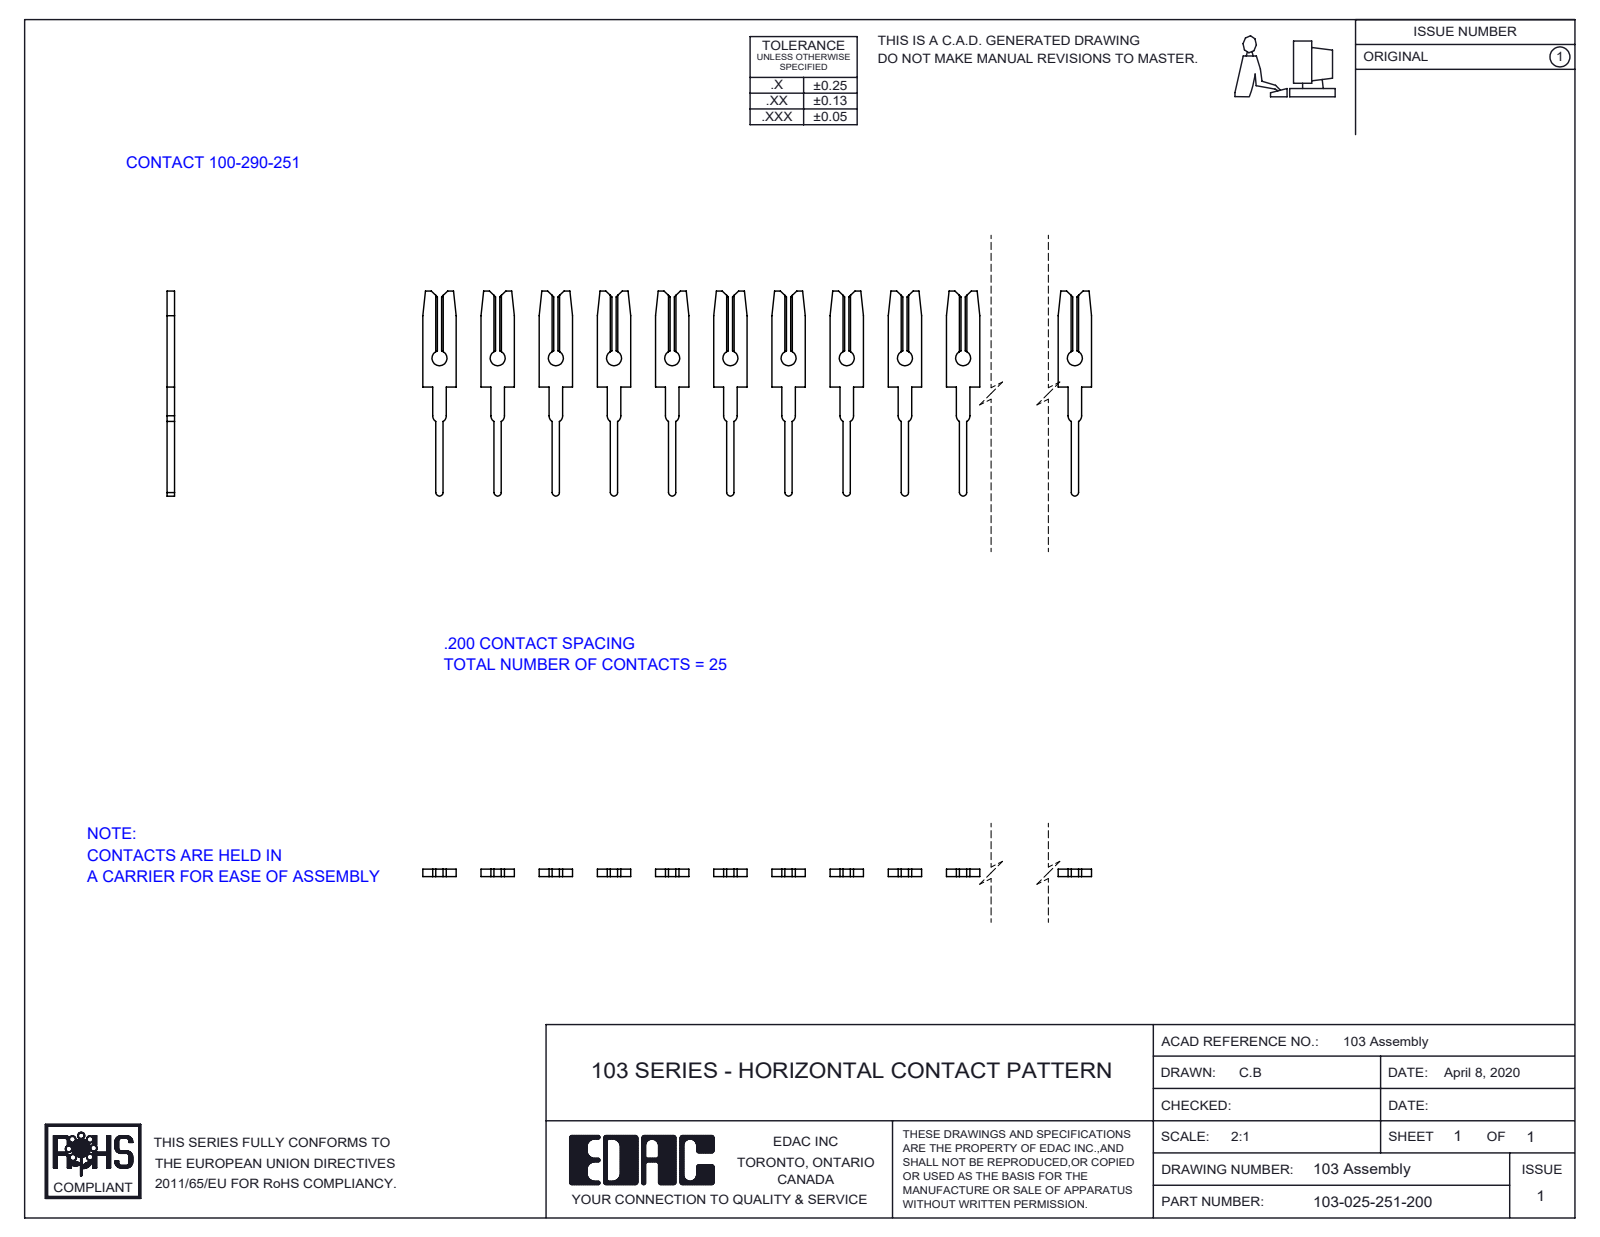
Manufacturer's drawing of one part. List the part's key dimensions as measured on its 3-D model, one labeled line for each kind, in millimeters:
Part name (STEP PRODUCT): 103-025-251-200; 100-290-001_100-290-251
STEP written by: SolidWorks 2016 (CONFIG_CONTROL_DESIGN)
Units: millimetres
Bodies: 25 solids, 700 faces (550 planar, 150 cylindrical, 0 other)
Overall size (bounding box): 124.8 × 17.9 × 0.7
Volume: 460 mm³ · Surface area: 2 246 mm²
Round holes (diameter × count): ⌀1.3 ×25
Partial cylindrical surfaces — rounded edges, fillets, slot ends (radius × count): R0.3 ×25, R0.6 ×25
Main face-to-face distances: 0.7, 3.6, 5.1, 10.2, 7.2, 21.5, 15.2, 25.1, 18, 20.3
Hole centre spacings: 5.1, 10.2, 15.2, 20.3, 25.4, 30.5, 35.6, 40.6
